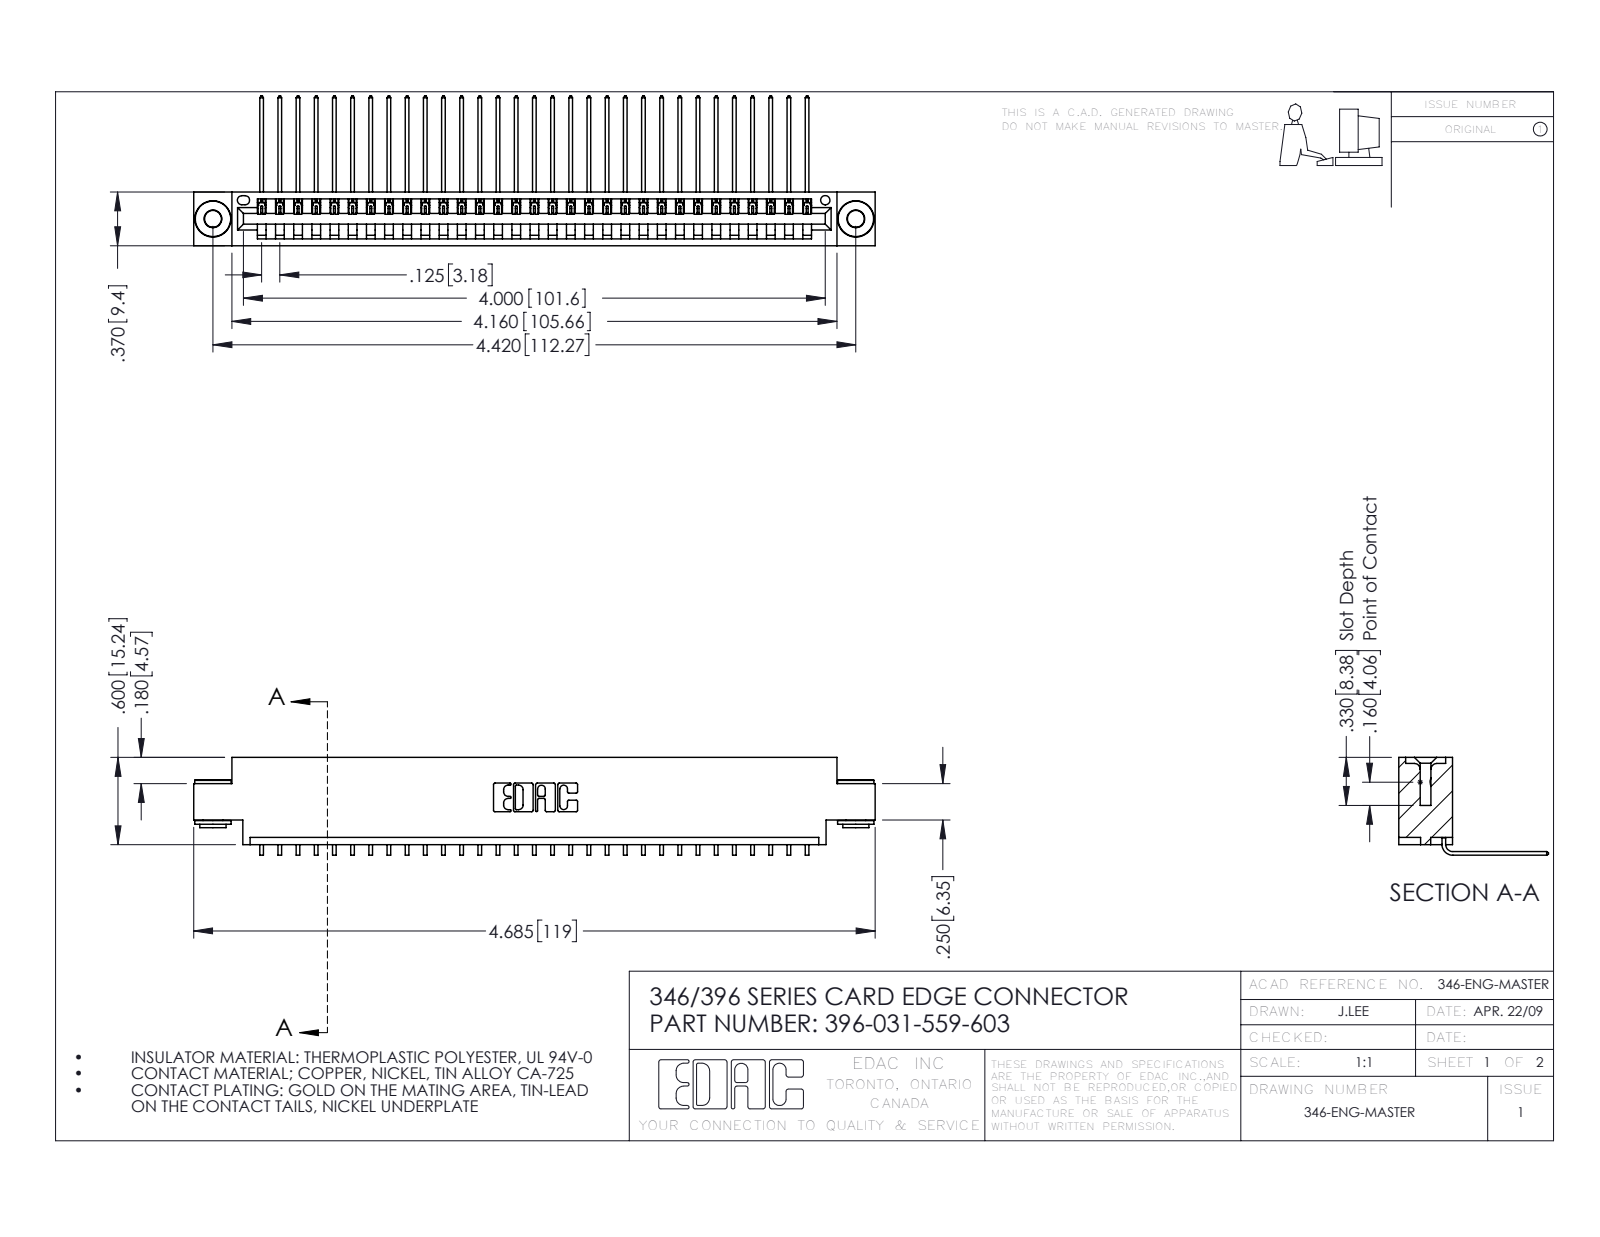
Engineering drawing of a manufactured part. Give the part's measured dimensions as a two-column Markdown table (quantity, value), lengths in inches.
| quantity | value |
| --- | --- |
| part name | 345-250-002_345-250-002-102; 345-292-001_558 559 Tail - 1; 346 Part_0.170 Offset - 0.156 Dia-TH; 396-031-559-603 |
| STEP written by | SolidWorks 2016 (CONFIG_CONTROL_DESIGN) |
| units | inches |
| bodies | 34 solids, 2024 faces (1392 planar, 624 cylindrical, 8 other) |
| overall size | 4.685 × 1.03 × 0.673 |
| volume | 0.689 in³ |
| surface area | 23.22 in² |
| round holes (diameter × count) | 0.116 × 2, 0.156 × 2, 0.064 × 1 |
| round bosses / shafts (diameter × count) | 0.25 × 2, 0.18 × 2, 0.136 × 2 |
| partial cylindrical surfaces (radius × count) | 0.006 × 62, 0.01 × 22, 0.007 × 6, 0.031 × 6, 0.026 × 3, 0.031 × 2, 0.04 × 2, 0.014 × 1 |
| main face-to-face distances | 0.048, 0.322, 0.37, 0.025, 0.25, 0.072, 0.298, 0.148, 0.222, 0.1 |
| hole center spacings | 0.246, 4.212, 4.42 |
